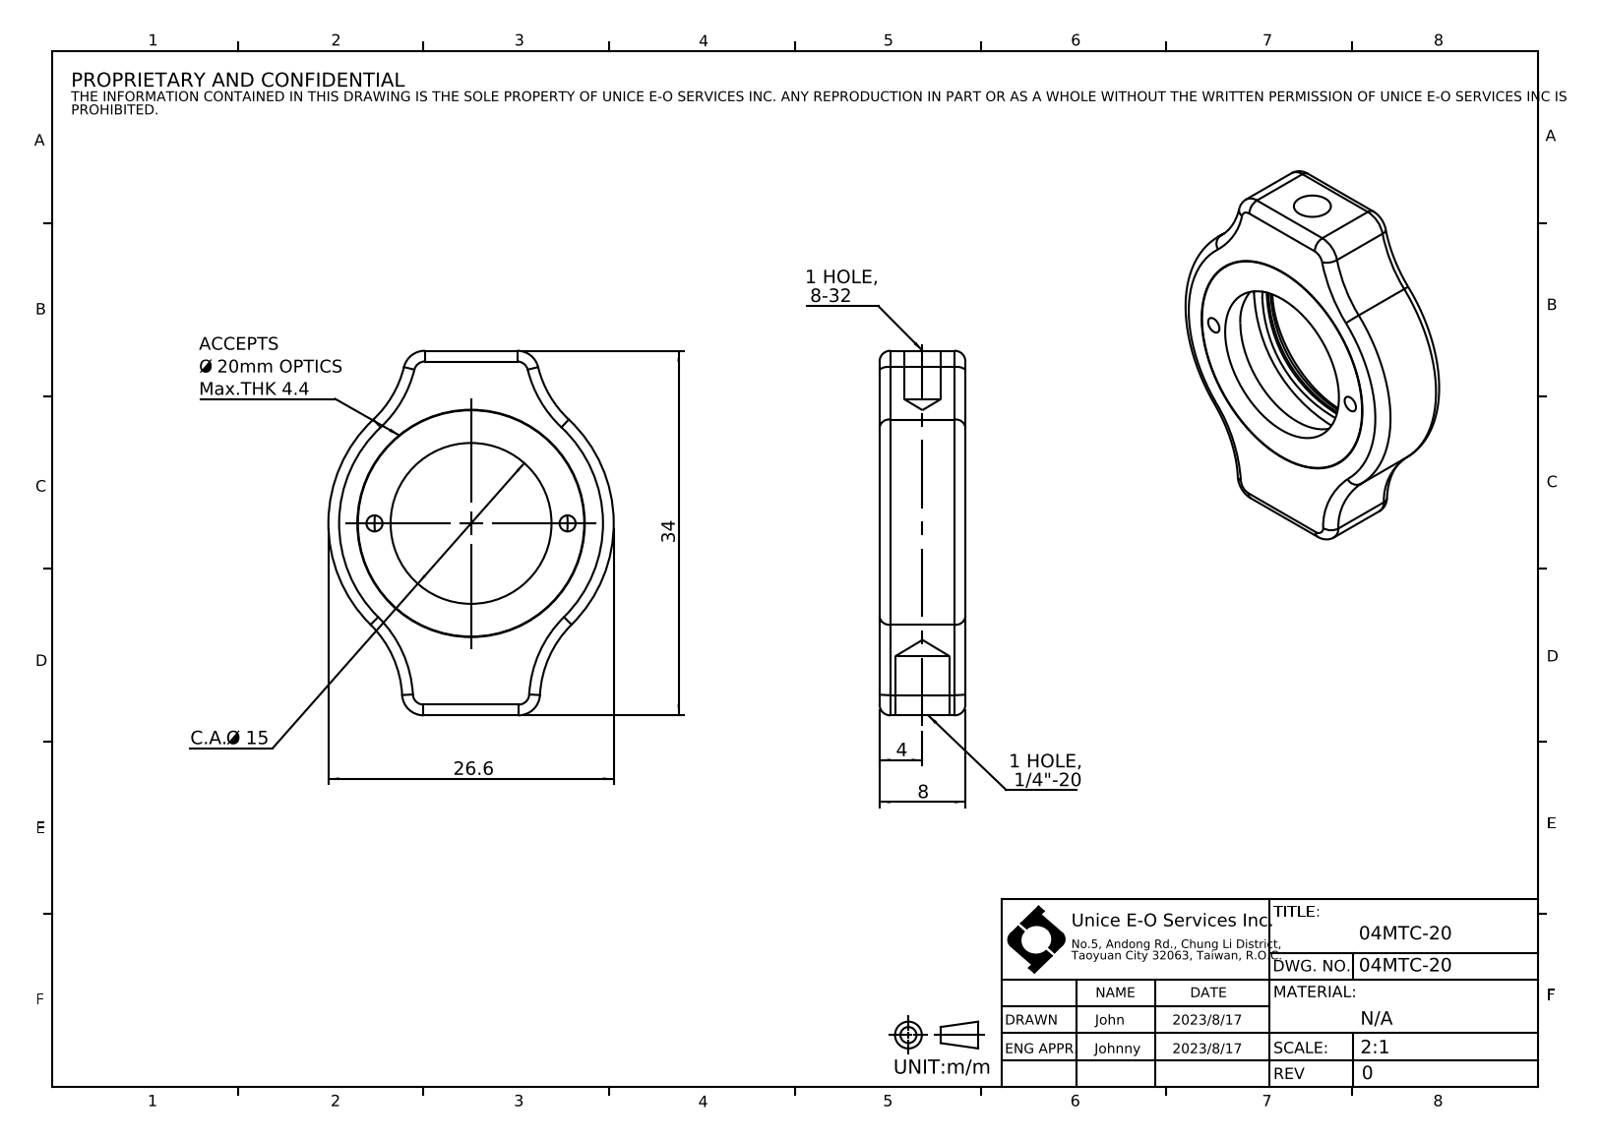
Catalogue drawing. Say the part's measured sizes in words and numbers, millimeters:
The part is named "04MTC-20". Its 3-D file was written by "SolidWorks 2016 (CONFIG_CONTROL_DESIGN)". It is 3 solids with 78 faces: 9 planar, 35 cylindrical and 34 other. Overall it measures 34 by 26.6 by 8 millimeters. Its volume is 3 020 cubic millimeters and its surface area 2 922 square millimeters. Round holes: 2 of diameter 1.5, 1 of diameter 3.45, 1 of diameter 5.11, 1 of diameter 15, 1 of diameter 18, 1 of diameter 20.2. Round bosses or shafts: 1 of diameter 21.1. Partial cylindrical surfaces (rounded edges, fillets, slot ends): 4 of radius 1, 4 of radius 2, 4 of radius 10, 1 of radius 13.3. The main face-to-face distances are 8, 2, 6, 7, 5, 1, 6.4, 4.4, 0.6, 1.6. The hole center spacings are 9, 18.
